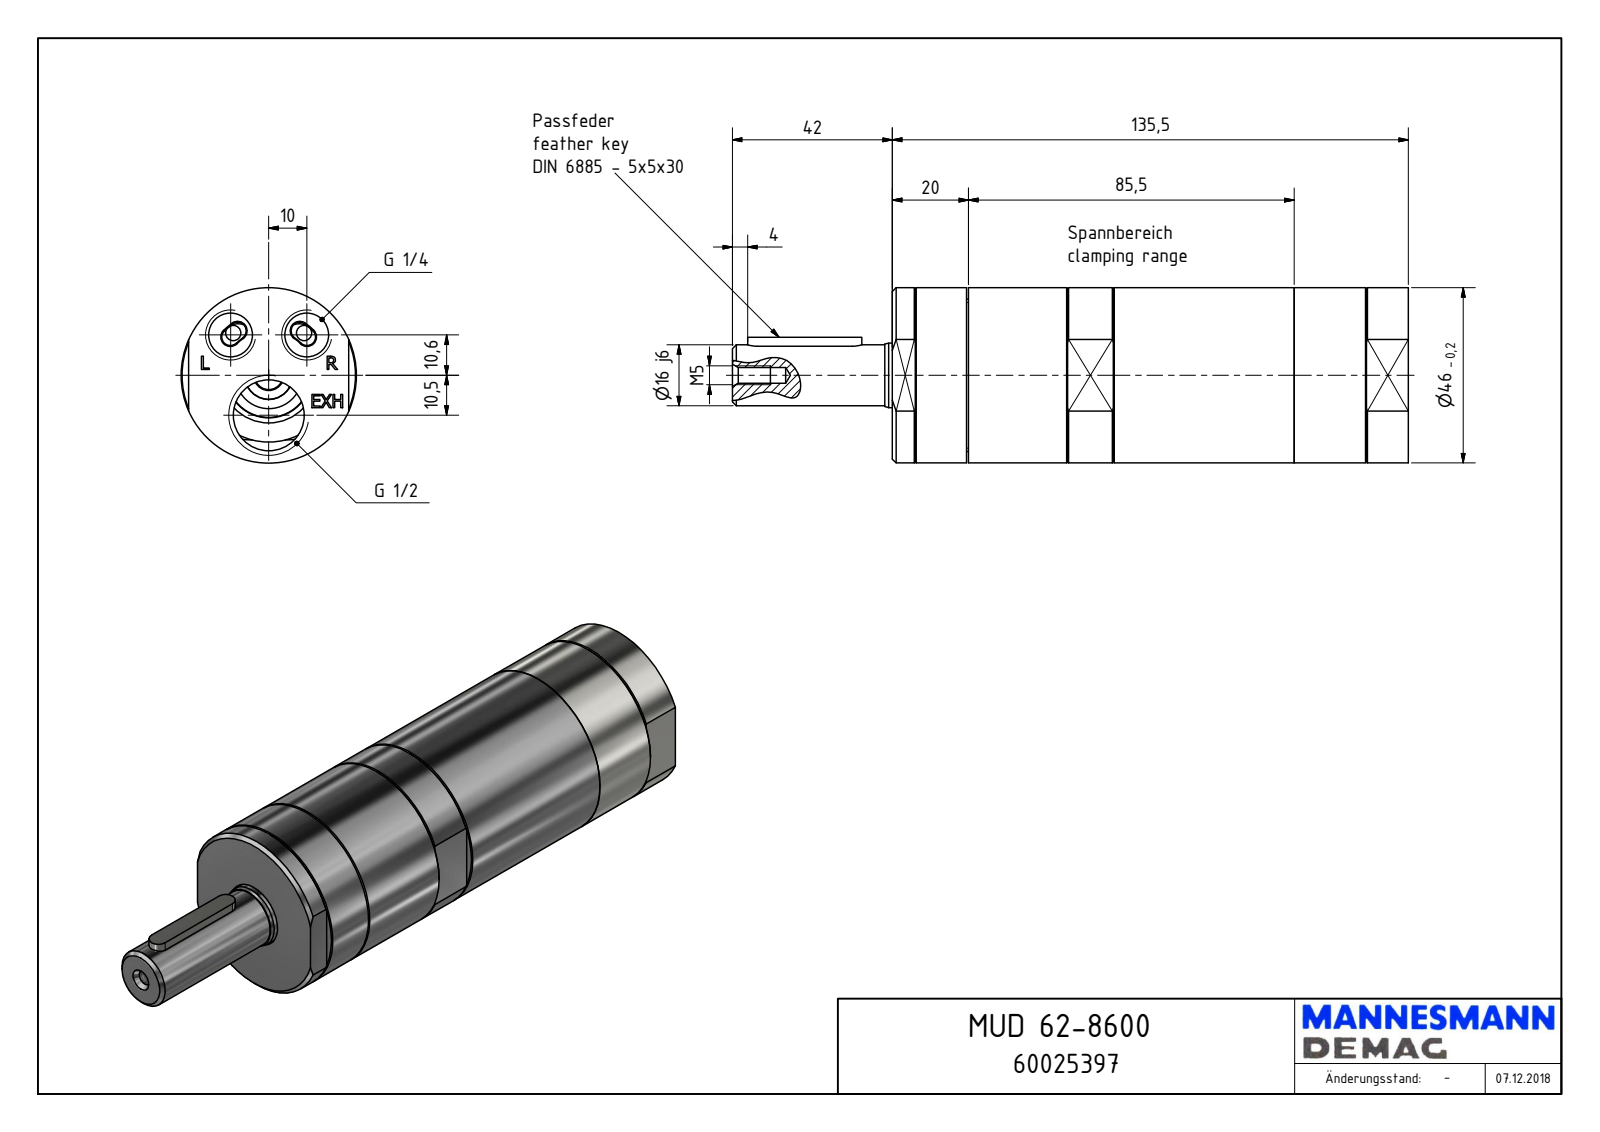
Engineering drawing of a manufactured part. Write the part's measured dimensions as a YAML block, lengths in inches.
part_name: "MUD 62-8600_60025397"
step_written_by: "Autodesk Inventor 2018 (AUTOMOTIVE_DESIGN)"
units: inches
bodies: {solids: 1, faces: 166, planar: 97, cylindrical: 36, other: 33}
overall_size: [6.988, 1.811, 1.811]
volume: 13.87
surface_area: 45.22
round_holes:
  - {diameter: 0.451, count: 2}
  - {diameter: 0.163, count: 1}
  - {diameter: 0.689, count: 1}
  - {diameter: 0.733, count: 1}
  - {diameter: 0.846, count: 1}
  - {diameter: 0.906, count: 1}
round_bosses_or_shafts:
  - {diameter: 1.811, count: 1}
  - {diameter: 1.575, count: 1}
  - {diameter: 1.299, count: 1}
  - {diameter: 0.77, count: 1}
  - {diameter: 0.667, count: 1}
  - {diameter: 0.63, count: 1}
partial_cylinders:
  - {radius: 0.098, count: 6}
  - {radius: 0.197, count: 2}
  - {radius: 0.659, count: 1}
  - {radius: 0.748, count: 1}
face_to_face_distances: [5.335, 1.654, 0.768, 0.787, 0.02, 4.567, 4.547, 5.061, 4.293, 4.273]
hole_center_spacings: [0.574, 0.919, 0.413, 0.787]
